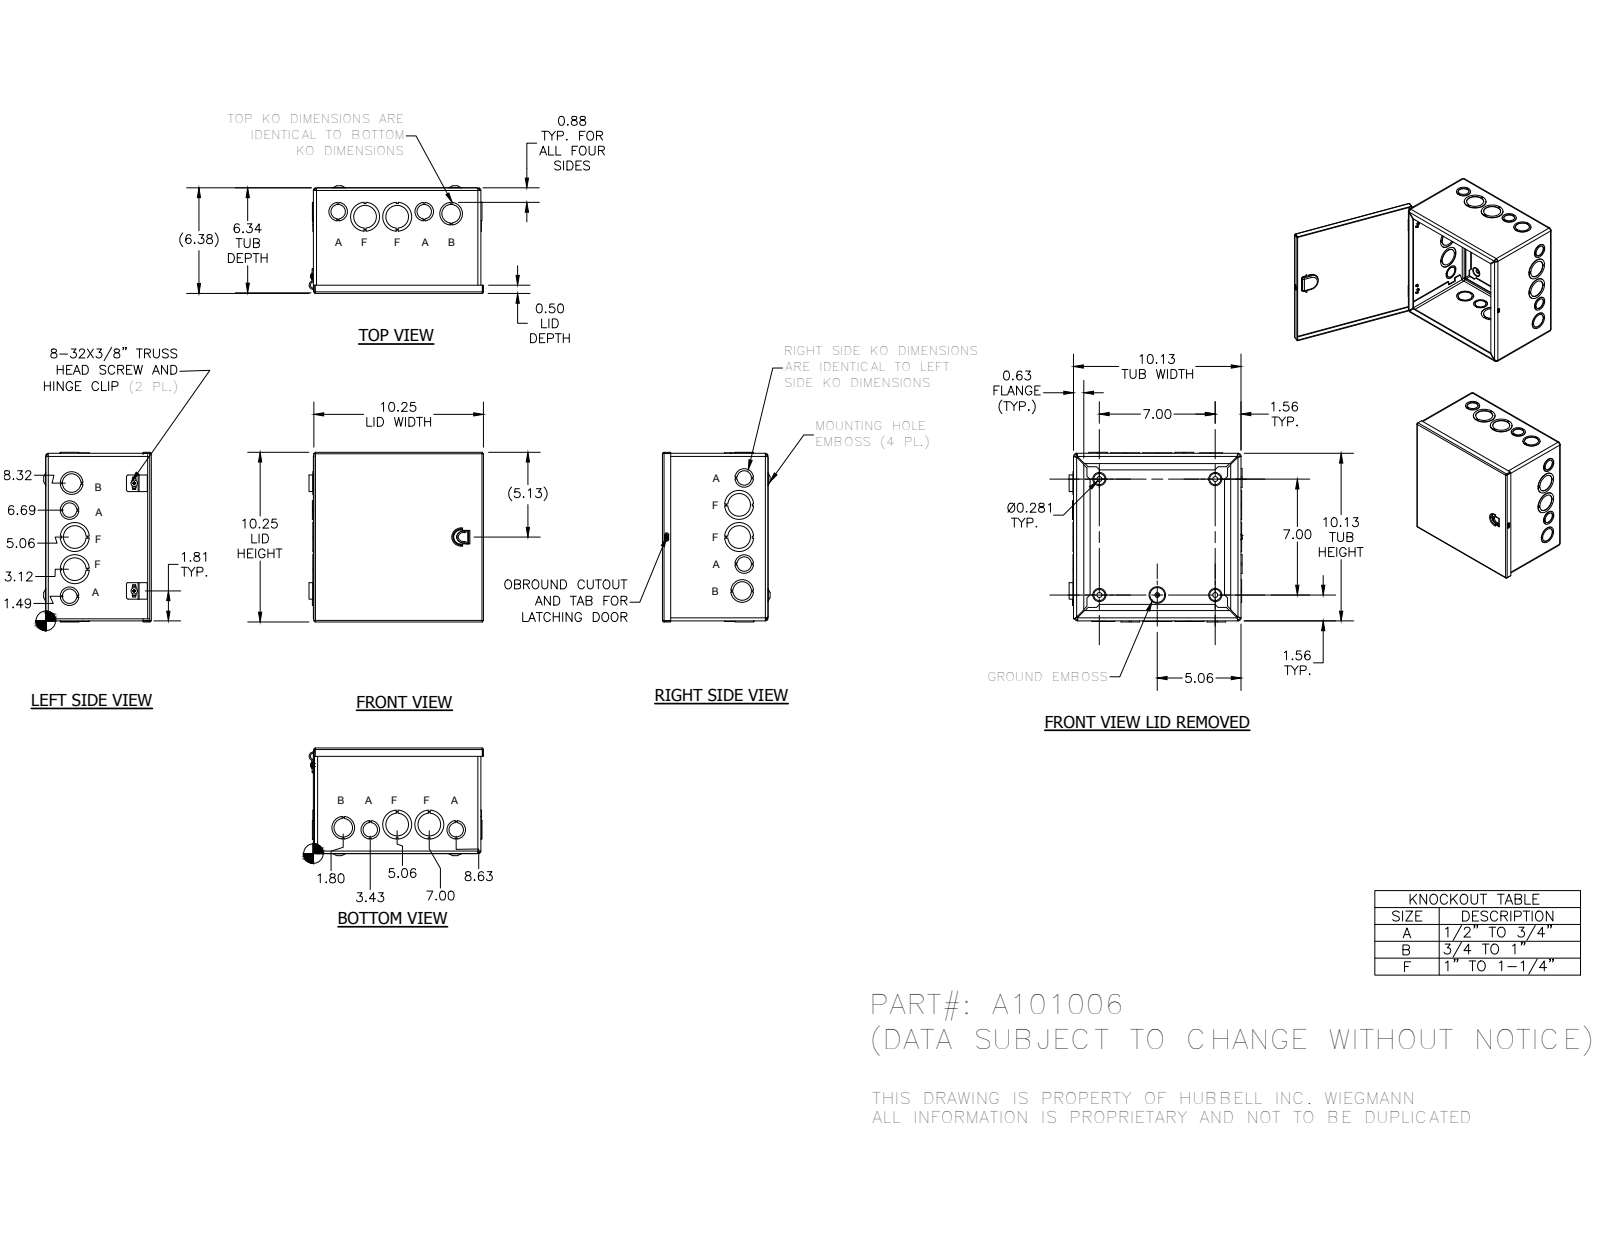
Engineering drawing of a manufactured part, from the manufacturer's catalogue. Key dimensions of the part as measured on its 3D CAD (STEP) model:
Part name (STEP PRODUCT): A1010BA; A101006WRA; 31816; 372177 (+3 more)
STEP written by: Autodesk Inventor 2014 (AUTOMOTIVE_DESIGN)
Units: millimetres
Bodies: 23 solids, 1055 faces (670 planar, 227 cylindrical, 158 other)
Overall size (bounding box): 265.44 × 260.35 × 165.19
Round holes (diameter × count): ⌀28.57 ×12, ⌀34.92 ×10, ⌀22.22 ×8, ⌀44.45 ×6, ⌀7.62 ×4, ⌀3.56 ×2, ⌀4.19 ×1
Round bosses / shafts (diameter × count): ⌀9.75 ×2, ⌀4.17 ×2, ⌀5.8 ×1
Partial cylindrical surfaces — rounded edges, fillets, slot ends (radius × count): R3.17 ×15, R0.79 ×10, R1.59 ×9, R2.38 ×8, R4.75 ×8, R1.4 ×4, R1.57 ×4, R1.78 ×4
Main face-to-face distances: 1.57, 1.58, 255.6, 254.03, 1.59, 160.43, 158.85, 160.44, 162.02, 257.18
Hole centre spacings: 42.15, 49.28, 91.03, 33.87, 132.08, 132.17, 177.8, 8.48
